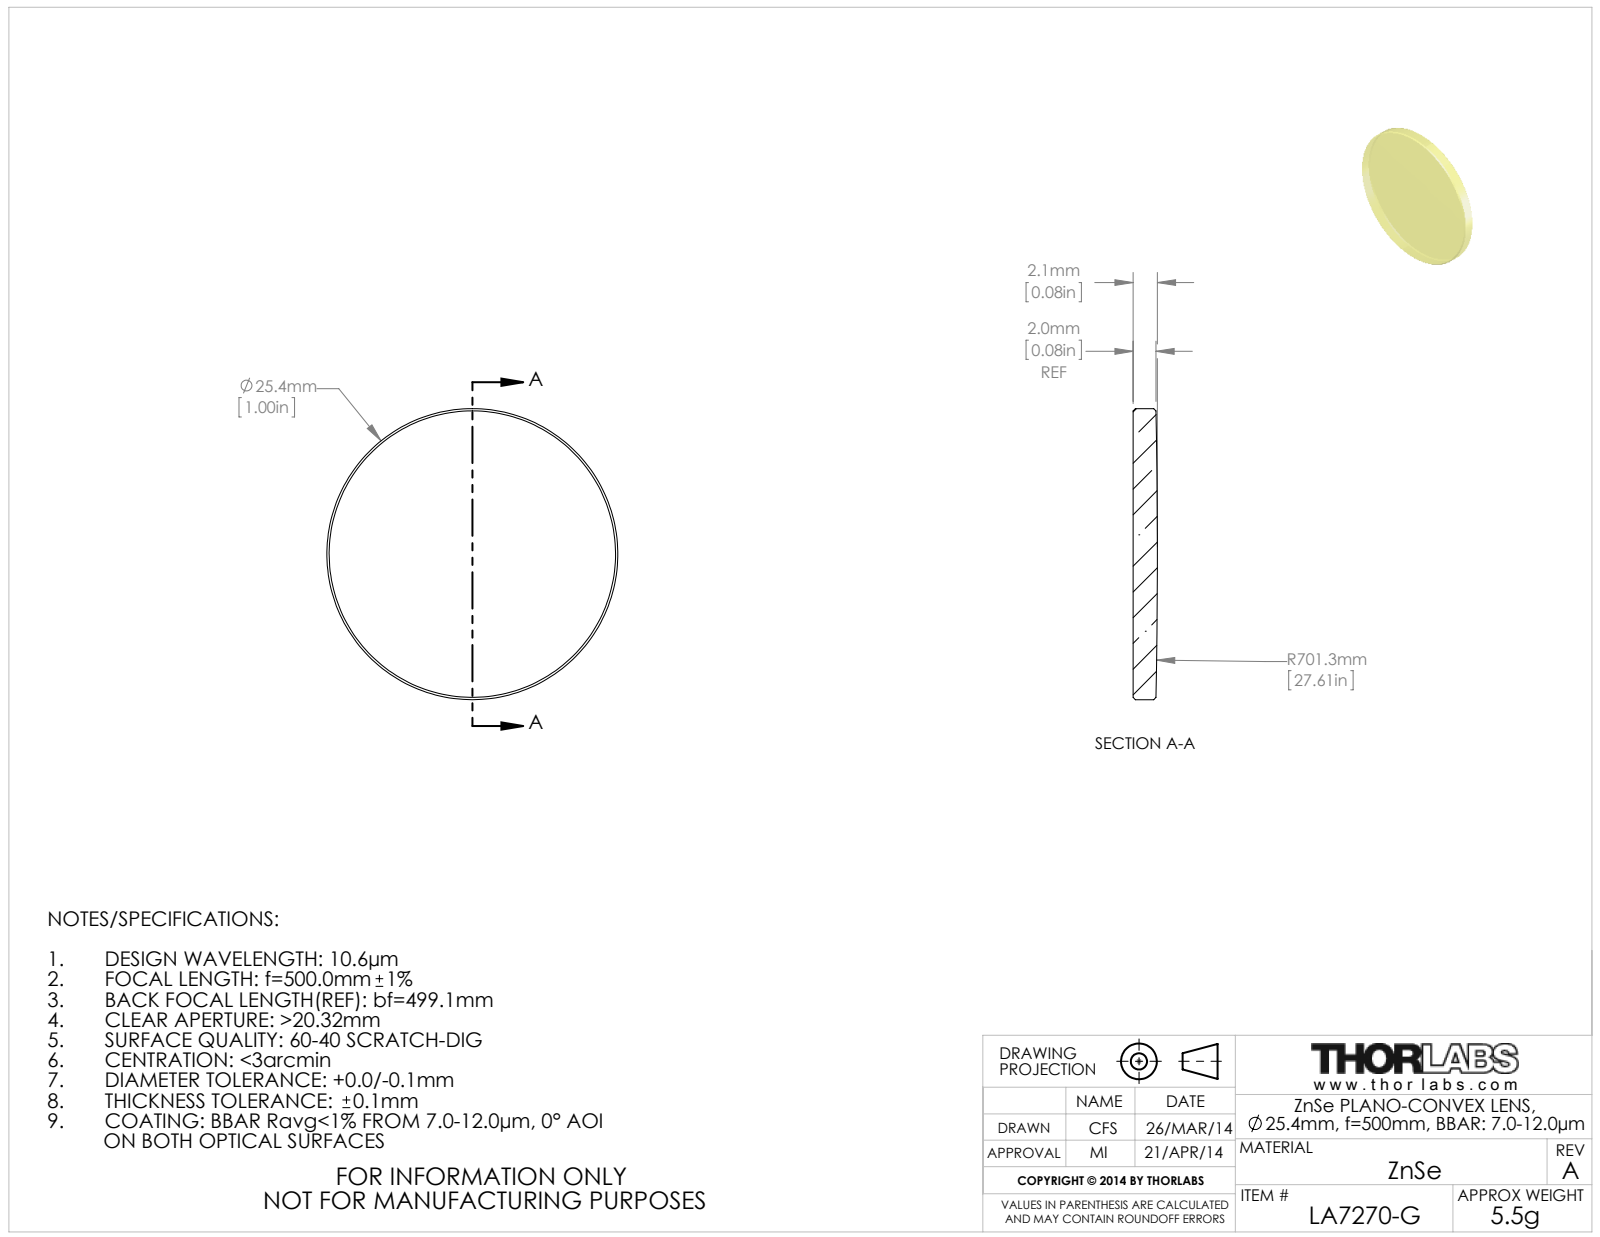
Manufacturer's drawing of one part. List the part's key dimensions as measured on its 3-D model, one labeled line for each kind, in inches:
Part name (STEP PRODUCT): TTN023918-E0W
STEP written by: SolidWorks 2012 (CONFIG_CONTROL_DESIGN)
Units: inches
Bodies: 1 solid, 9 faces (1 planar, 2 cylindrical, 6 other)
Overall size (bounding box): 1 × 1 × 0.083
Volume: 0.063 in³ · Surface area: 1.789 in²
Round bosses / shafts (diameter × count): ⌀1 ×1
